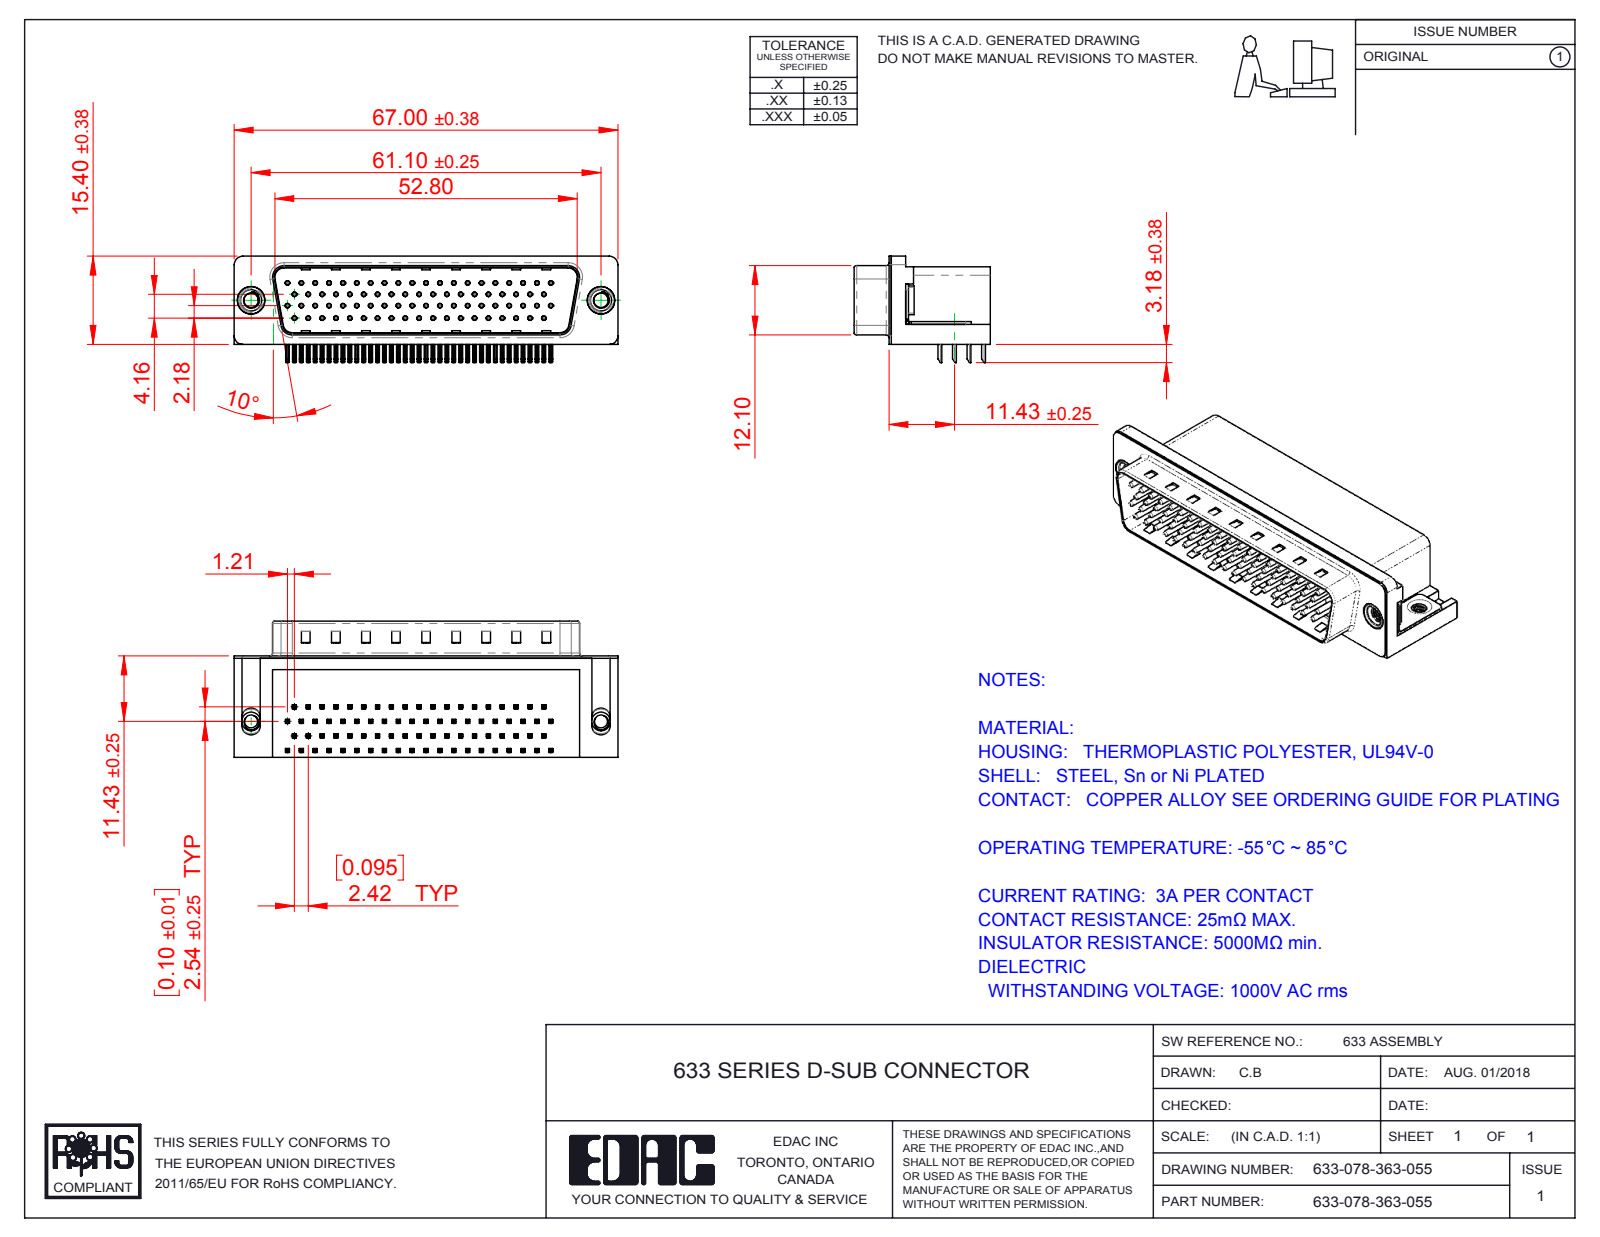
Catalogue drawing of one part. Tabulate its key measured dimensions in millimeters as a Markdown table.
| quantity | value |
| --- | --- |
| part name | 633 Contact Top_78 Contact; 633 Contact Middle_78 Contact; 633 Shell_78 Contact; 633-078-363-055 (+5 more) |
| STEP written by | SolidWorks 2016 (CONFIG_CONTROL_DESIGN) |
| units | millimeters |
| bodies | 84 solids, 6306 faces (3981 planar, 1794 cylindrical, 531 other) |
| overall size | 67 × 23.8 × 18.58 |
| volume | 14 619 mm³ |
| surface area | 16 431 mm² |
| round holes (diameter × count) | 0.35 × 78, 0.8 × 78, 2.26 × 2, 2.5 × 2, 4 × 2, 4.8 × 2, 5 × 2 |
| round bosses / shafts (diameter × count) | 0.75 × 78, 4.9 × 2, 4.75 × 2, 3.9 × 2, 3.26 × 2 |
| partial cylindrical surfaces (radius × count) | 0.25 × 320, 0.12 × 156, 1 × 16, 0.5 × 9, 1.6 × 8, 1.5 × 6, 0.45 × 4, 0.9 × 4 |
| main face-to-face distances | 0.4, 13.2, 17.3, 11.7, 13.35, 2.05, 13.75, 1.65, 1.85, 11.9 |
| hole center spacings | 2.42, 4.84, 7.26, 9.68, 6.26, 7.13, 12.1, 8.62 |
